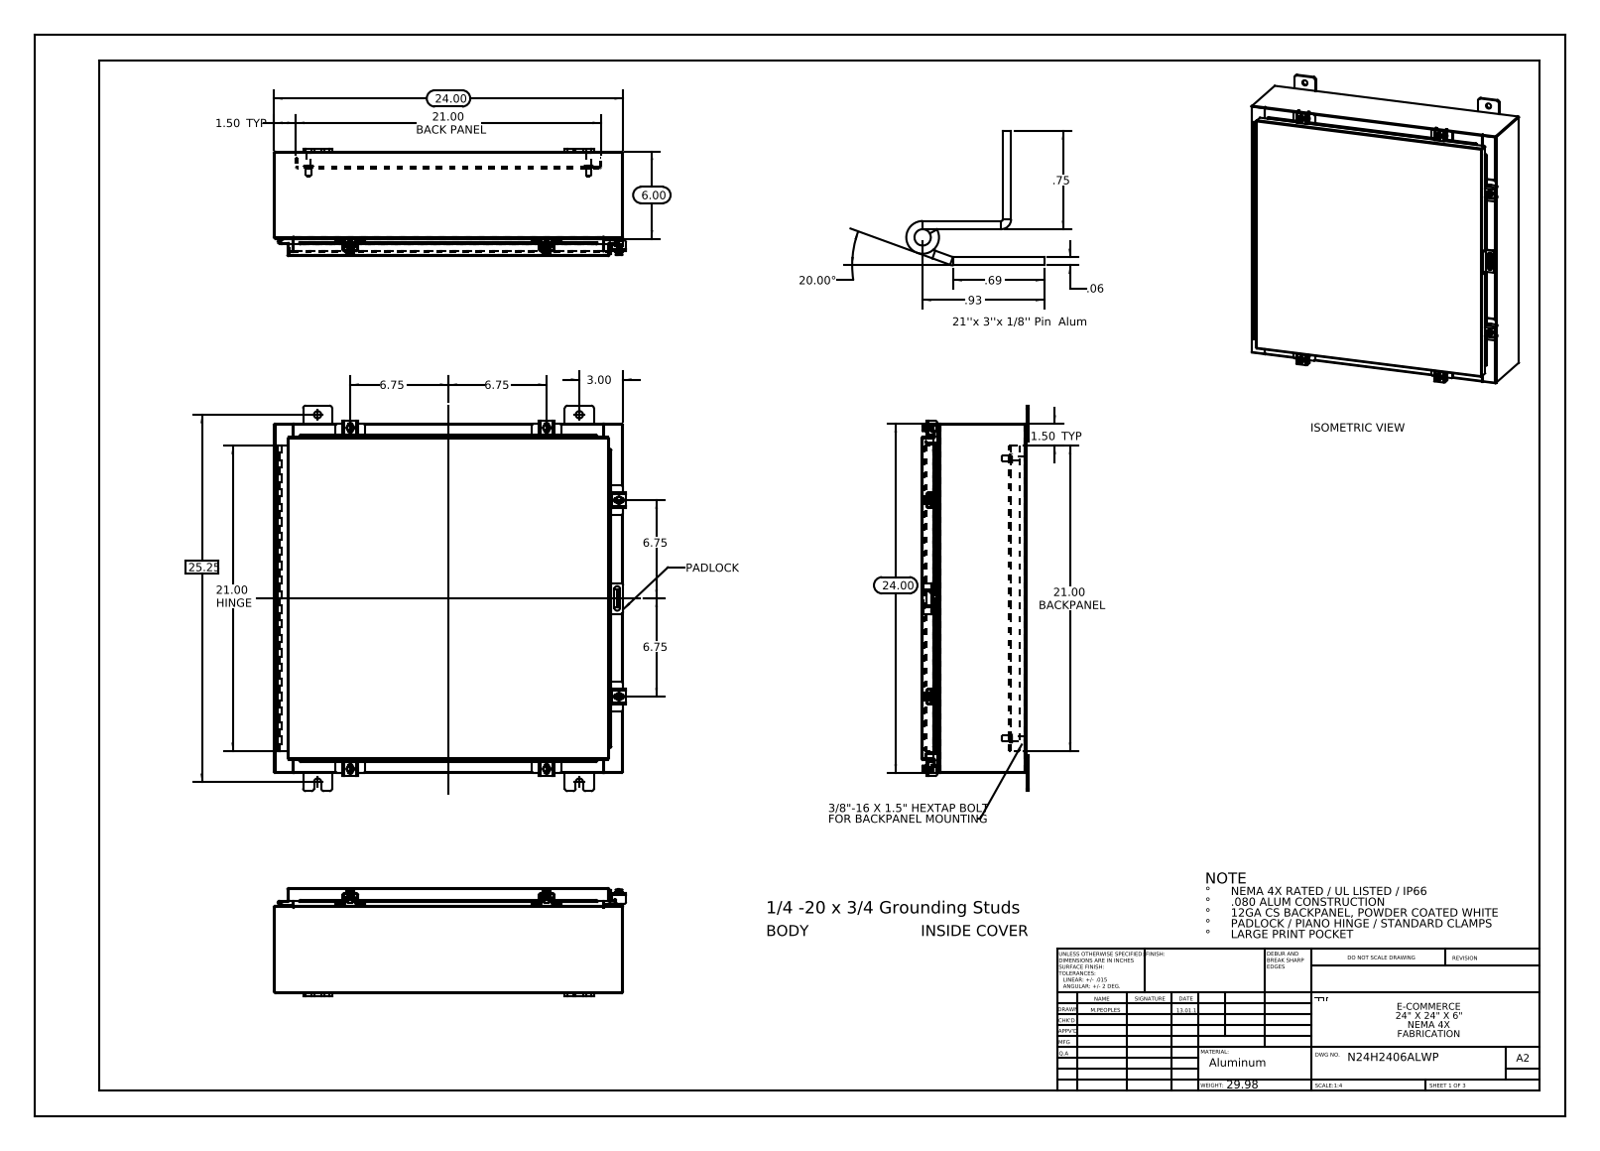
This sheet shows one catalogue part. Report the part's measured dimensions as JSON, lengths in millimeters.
{"part_name": "N24H2406ALWP; N24H2406ALWP Clamp Top; N24H2406ALWP Padlock Staple; N24H2406ALWP Cover (+8 more)", "step_written_by": "SolidWorks 2013 (CONFIG_CONTROL_DESIGN)", "units": "millimeters", "bodies": {"solids": 47, "faces": 1709, "planar": 908, "cylindrical": 705, "other": 96}, "overall_size": [673.1, 615, 187.7], "volume_mm3": 3309000, "surface_area_mm2": 3257000, "round_holes": [[12.7, 8], [5.4, 6], [6.6, 6], [3.2, 2], [3.2, 1]], "round_bosses_or_shafts": [[6.4, 7], [12.7, 6], [10.1, 6], [15.9, 4], [9.5, 4], [8.4, 4]], "partial_cylinders_radius": [[1.5, 30], [0.3, 25], [4.8, 24], [2.2, 21], [3, 12], [3.6, 12], [3.2, 10], [1.3, 9]], "face_to_face_distances": [1.9, 181, 607.7, 182.9, 179.1, 2.6, 25.4, 27.3, 153.7, 155.6], "hole_center_spacings": [419.3, 486, 547.2, 683.4, 342.9, 47.2, 57.8, 61.5]}
